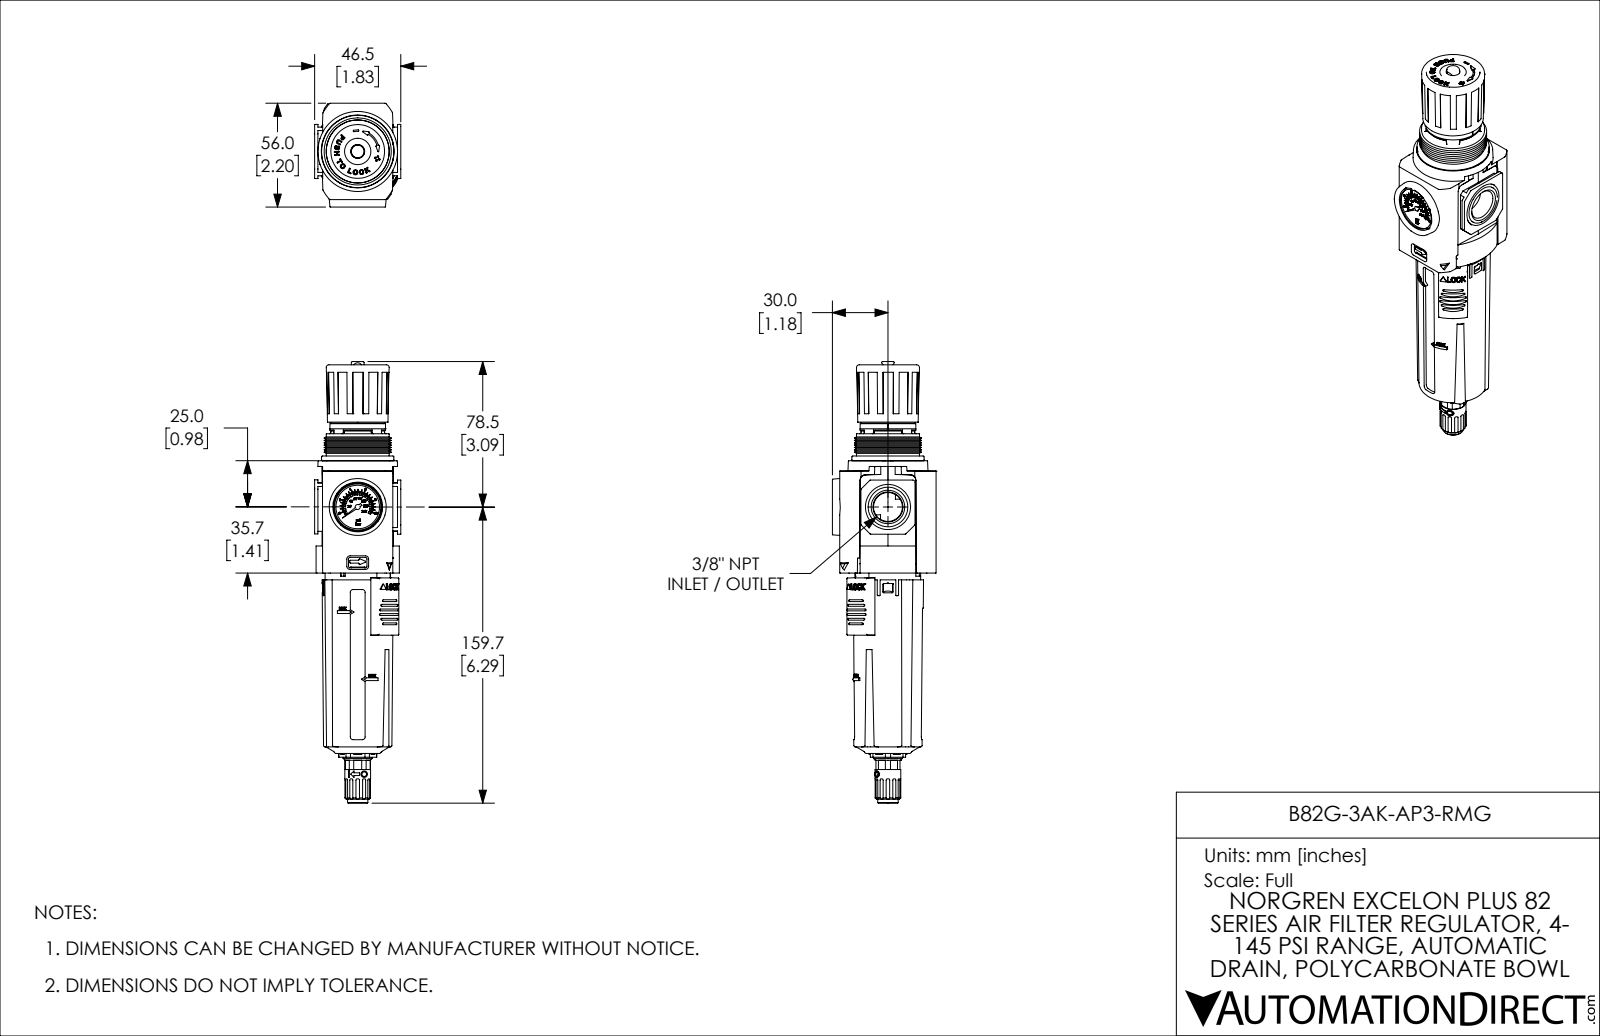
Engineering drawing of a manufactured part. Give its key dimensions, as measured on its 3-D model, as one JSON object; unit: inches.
{"part_name": "B82G-3AK-AP3-RMG", "step_written_by": "SolidWorks 2021 (CONFIG_CONTROL_DESIGN)", "units": "inches", "bodies": {"solids": 8, "faces": 2715, "planar": 1038, "cylindrical": 1255, "other": 422}, "overall_size": [9.379, 2.205, 1.831], "volume_in3": 17.36, "surface_area_in2": 113.9, "round_holes": [[0.097, 4], [0.138, 2], [0.098, 1], [0.128, 1], [0.197, 1], [0.236, 1], [0.259, 1], [0.63, 1], [0.925, 1], [1.102, 1], [1.354, 1]], "round_bosses_or_shafts": [[0.224, 2], [0.118, 2], [1.535, 1], [1.388, 1], [1.356, 1], [1.339, 1], [1.291, 1], [1.257, 1]], "partial_cylinders_radius": [[0.02, 55], [0.039, 42], [0.009, 25], [0.031, 20], [0.006, 19], [0.012, 15], [0.012, 12], [0.012, 12]], "face_to_face_distances": [0.059, 1.988, 1.693, 0.354, 1.634, 0.295, 1.417, 1.475, 0.182, 1.352], "hole_center_spacings": [0.63, 1.091, 1.26, 2.705, 3.325, 2.965, 5.374, 5.402]}
